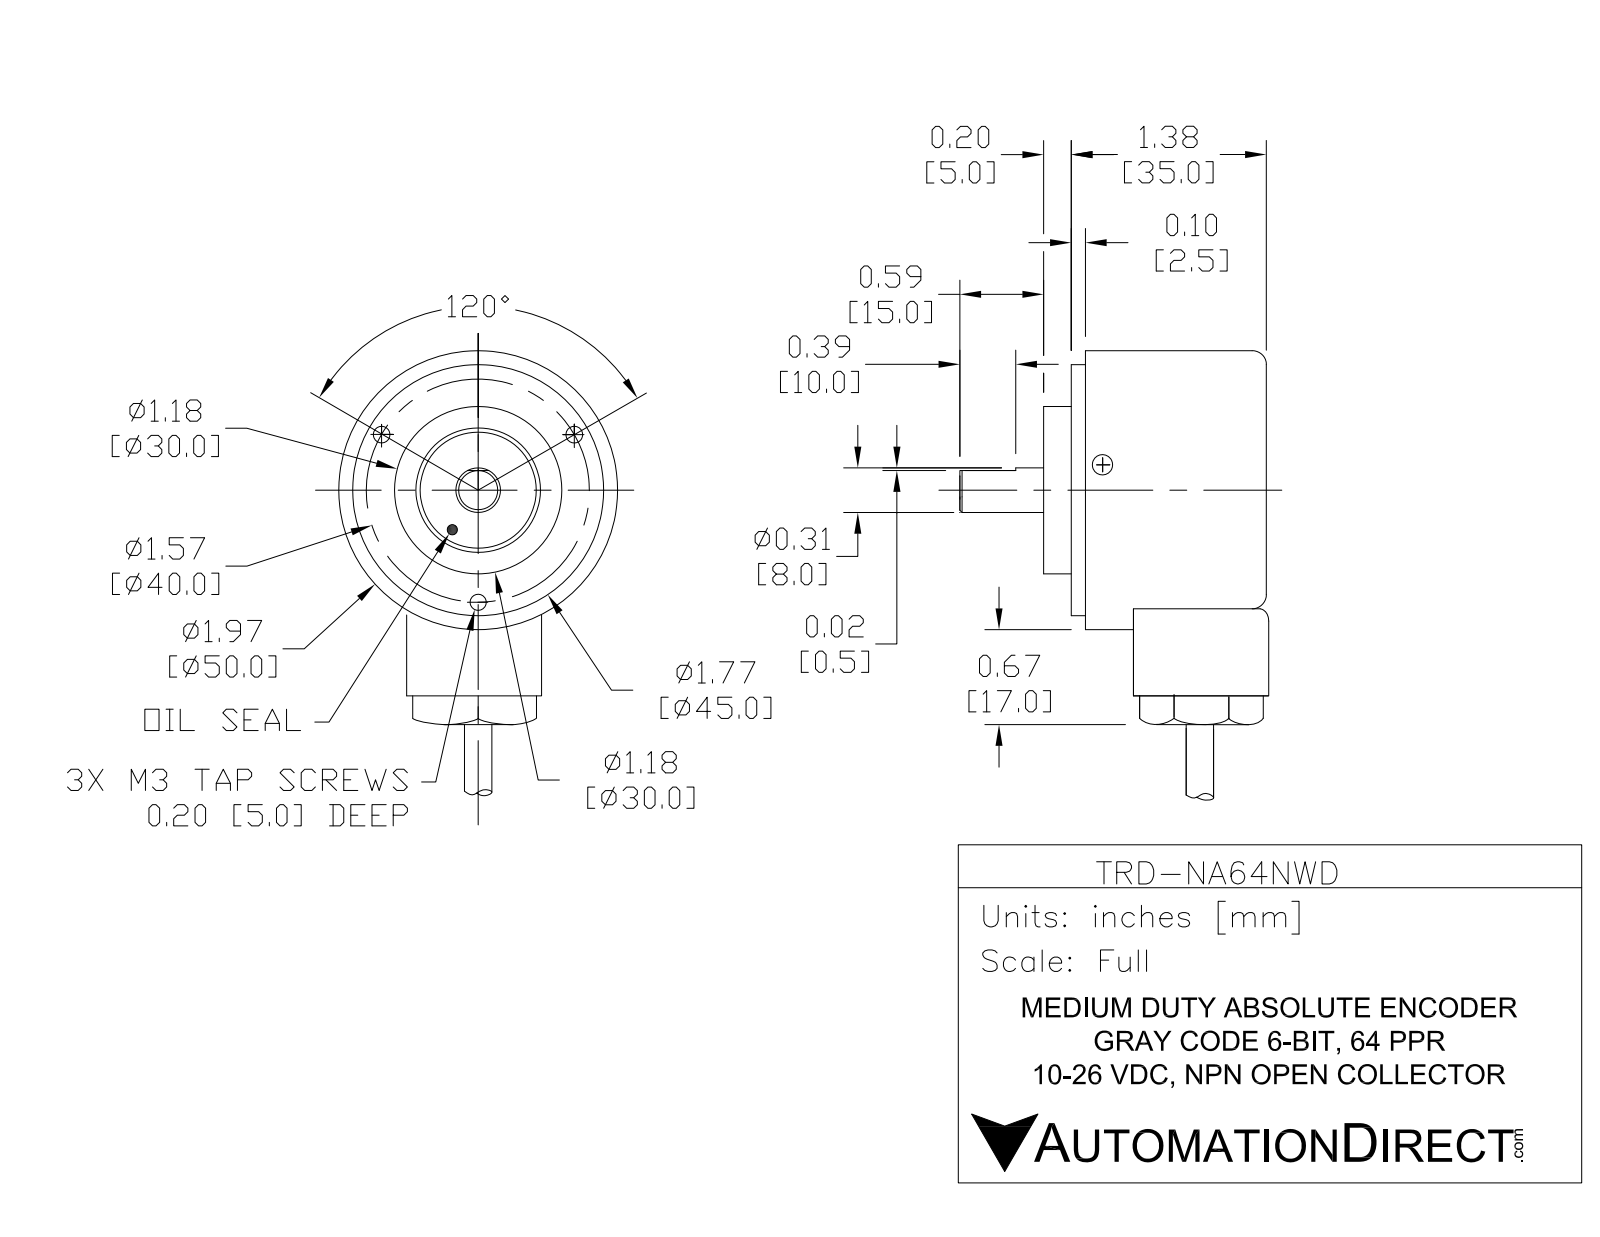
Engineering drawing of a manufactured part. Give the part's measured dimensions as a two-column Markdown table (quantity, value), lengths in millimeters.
| quantity | value |
| --- | --- |
| part name | TRD-NA-W |
| STEP written by | SolidWorks 2016 (AUTOMOTIVE_DESIGN) |
| units | millimeters |
| bodies | 2 solids, 168 faces (45 planar, 75 cylindrical, 48 other) |
| overall size | 135.5 × 103.66 × 50.02 |
| volume | 80 471 mm³ |
| surface area | 15 761 mm² |
| round holes (diameter × count) | 2.2 × 3, 2.5 × 3, 7.5 × 1 |
| round bosses / shafts (diameter × count) | 1.8 × 7, 1 × 7, 2 × 3, 7 × 2, 45 × 1, 30 × 1, 14 × 1, 12 × 1 |
| partial cylindrical surfaces (radius × count) | 0.2 × 4, 1 × 4, 24.1 × 1 |
| main face-to-face distances | 35, 5, 40, 32.5, 7.5, 2.5, 23, 18, 15.5, 17 |
| hole center spacings | 34.64 |
